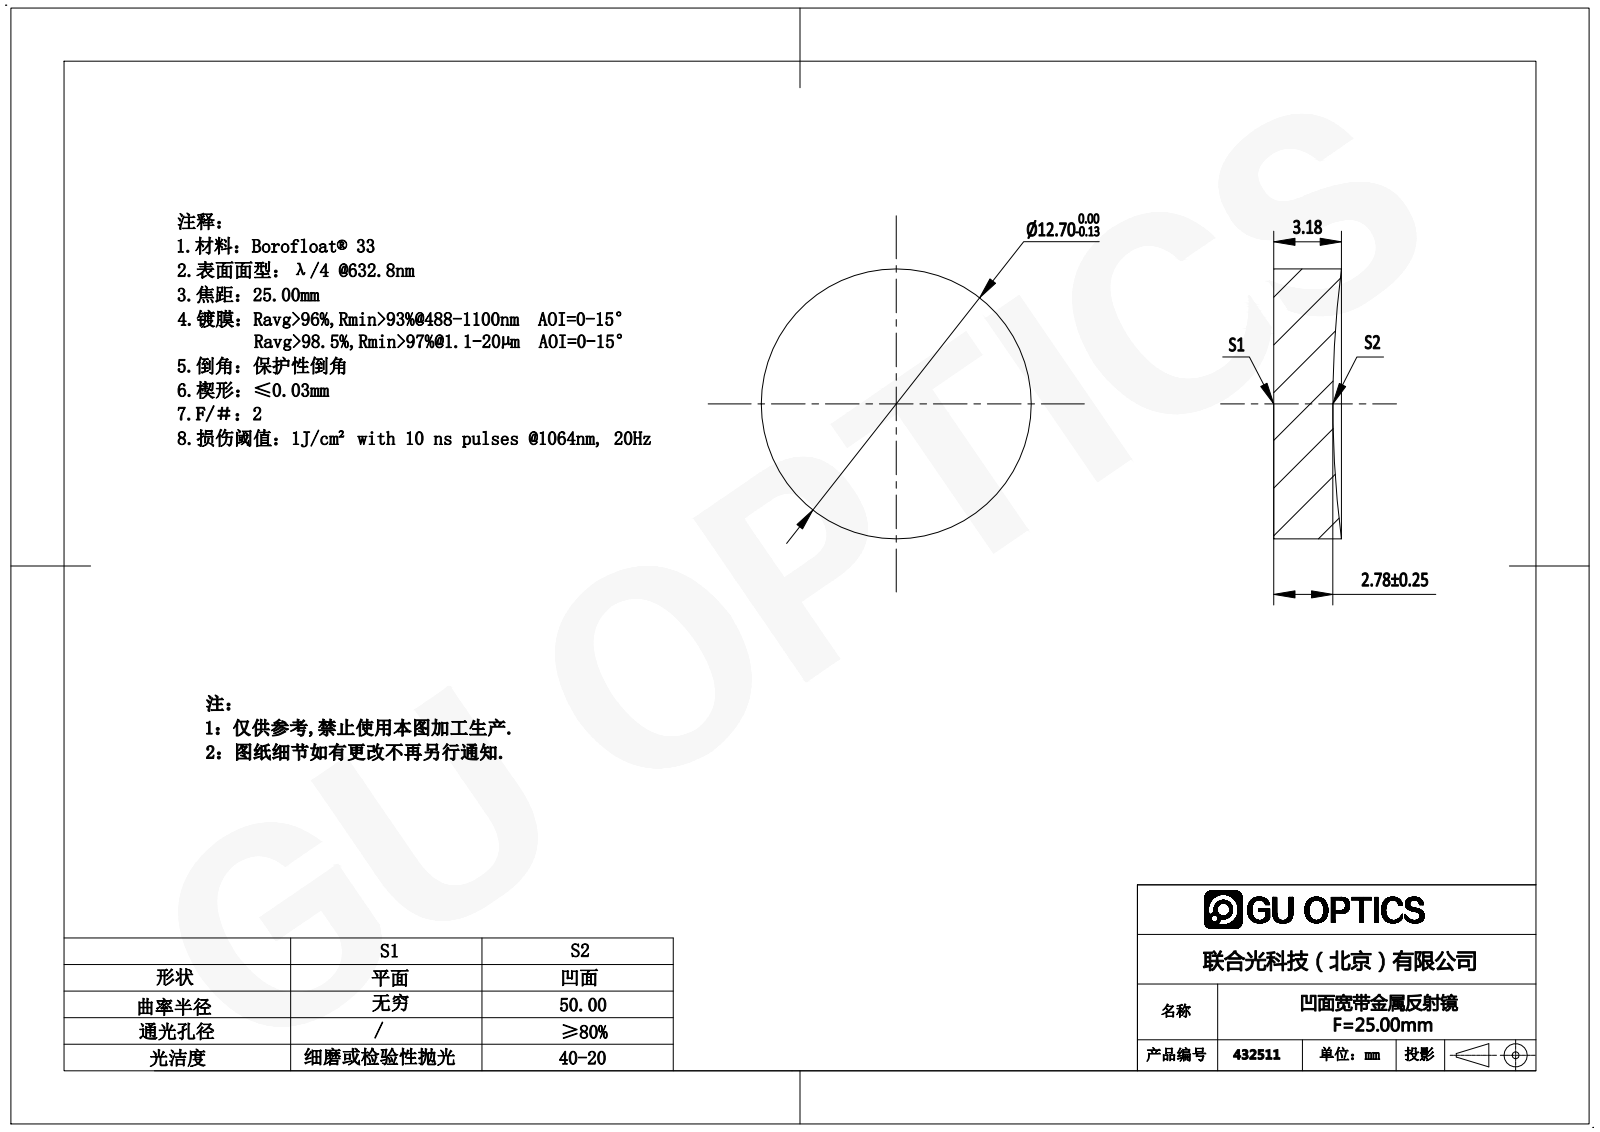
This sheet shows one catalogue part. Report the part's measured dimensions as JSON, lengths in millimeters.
{"part_name": "432501", "step_written_by": "SolidWorks 2016 (AUTOMOTIVE_DESIGN)", "units": "millimeters", "bodies": {"solids": 1, "faces": 5, "planar": 1, "cylindrical": 2, "other": 2}, "overall_size": [12.7, 12.7, 3.19], "volume_mm3": 378, "surface_area_mm2": 381, "round_bosses_or_shafts": [[12.7, 1]]}
